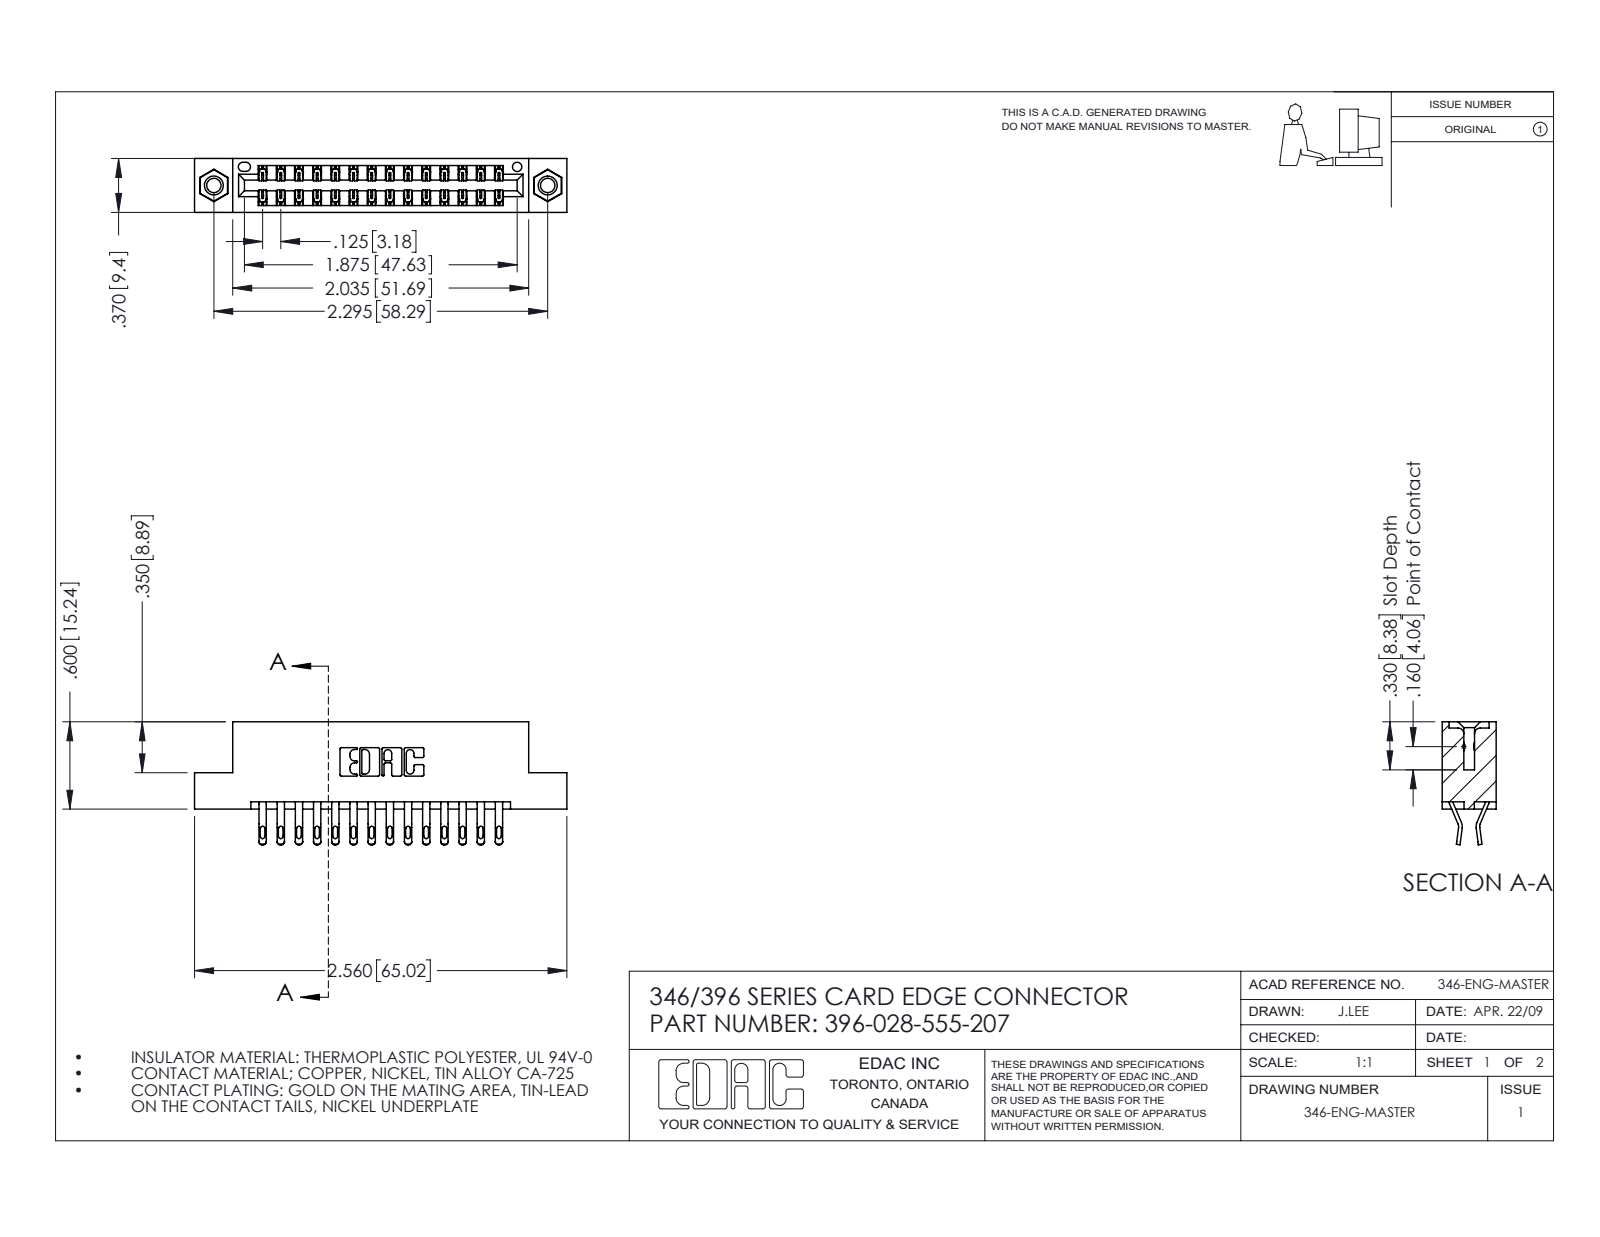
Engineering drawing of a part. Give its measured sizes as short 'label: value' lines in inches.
name: 346 Part_Flush Mounting Lugs - 0.156 Dia-TI; 396-028-555-207; 345-250-001_345-250-005-103; 345-292-001_555 Tail
written by: SolidWorks 2016 (CONFIG_CONTROL_DESIGN)
unit: in
bodies: 31 solids, 1806 faces (1032 planar, 758 cylindrical, 16 other)
size: 2.56 × 0.845 × 0.37
volume: 0.378 in³; area: 13.01 in²
holes: 2× ⌀0.098, 2× ⌀0.125, 2× ⌀0.156, 1× ⌀0.064
bosses: 2× ⌀0.155
rounds: 56× R0.016, 56× R0.02, 42× R0.006, 22× R0.01, 6× R0.007, 6× R0.031, 3× R0.026, 2× R0.01
face distances: 0.048, 0.322, 0.25, 0.37, 0.025, 0.072, 0.298, 0.275, 0.148, 0.222
hole spacings: 0.246, 2.089, 2.295
